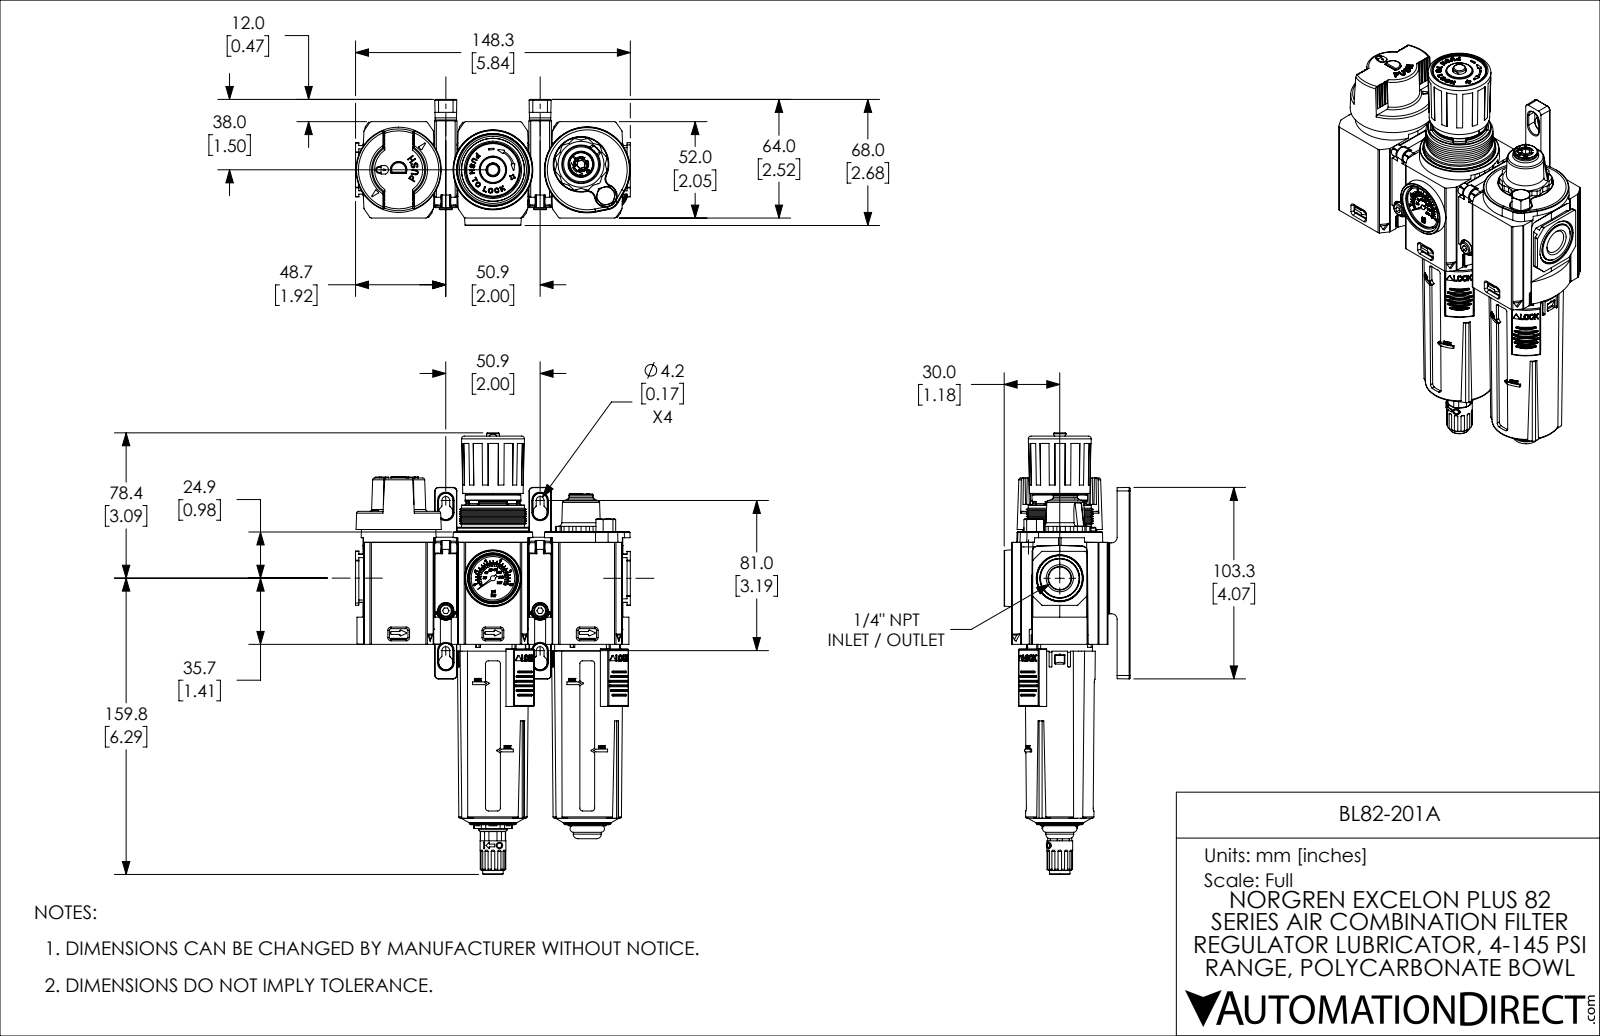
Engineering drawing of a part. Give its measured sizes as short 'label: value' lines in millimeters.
name: BL82-201A
written by: SolidWorks 2021 (CONFIG_CONTROL_DESIGN)
unit: mm
bodies: 20 solids, 5513 faces (2336 planar, 2178 cylindrical, 999 other)
size: 238.2 × 148.3 × 68
volume: 635 300 mm³; area: 209 800 mm²
holes: 4× ⌀2.5, 4× ⌀7.8, 2× ⌀1, 2× ⌀3.3, 2× ⌀3.5, 2× ⌀4.4, 2× ⌀4.7, 2× ⌀16, 1× ⌀2.5, 1× ⌀2.7, 1× ⌀3.3, 1× ⌀5
bosses: 4× ⌀7, 2× ⌀35.3, 2× ⌀34.4, 2× ⌀32.8, 2× ⌀31.9, 2× ⌀6.1, 2× ⌀5.7, 2× ⌀4
rounds: 153× R0.5, 148× R1, 32× R0.2, 29× R0.3, 27× R0.3, 26× R0.2, 25× R0.2, 25× R0.8
face distances: 1.5, 50.9, 50.5, 50.9, 52, 49, 101.7, 34.3, 4.6, 4.4
hole spacings: 16, 50.9, 14.1, 40.1, 15, 17.5, 25.5, 27.7
